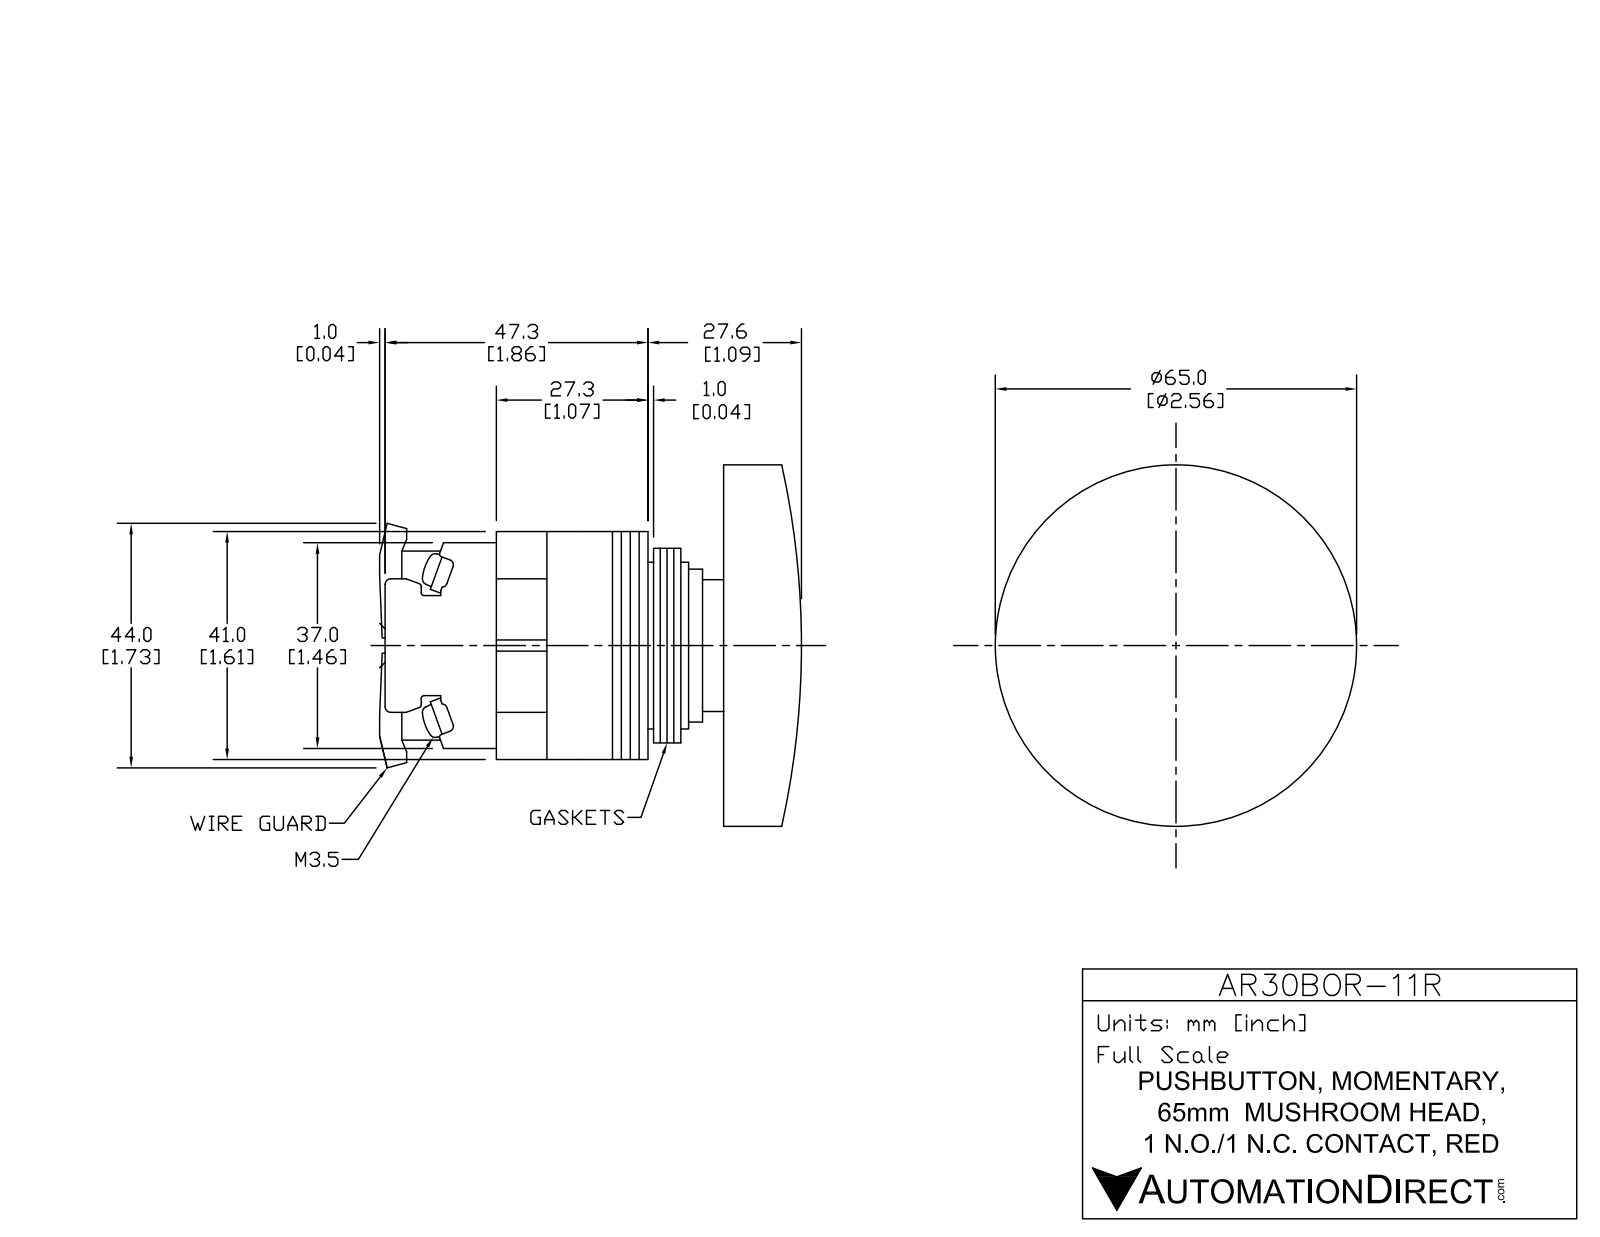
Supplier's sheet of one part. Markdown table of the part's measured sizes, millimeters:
| quantity | value |
| --- | --- |
| part name | AR30B0R-11R |
| STEP written by | SolidWorks 2017 (AUTOMOTIVE_DESIGN) |
| units | millimeters |
| bodies | 20 solids, 381 faces (236 planar, 127 cylindrical, 18 other) |
| overall size | 76 × 65 × 65 |
| volume | 83 080 mm³ |
| surface area | 42 286 mm² |
| round holes (diameter × count) | 3 × 4, 24 × 1, 30 × 1, 60 × 1 |
| round bosses / shafts (diameter × count) | 5 × 4, 65 × 1, 40 × 1, 35 × 1, 29.8 × 1 |
| partial cylindrical surfaces (radius × count) | 0.5 × 16, 5 × 10, 1.75 × 8, 2 × 4, 3 × 4 |
| main face-to-face distances | 1.6, 21, 16, 3.2, 41, 5, 1, 4.8, 36, 15.99 |
| hole center spacings | 21.92, 31, 43.84 |
